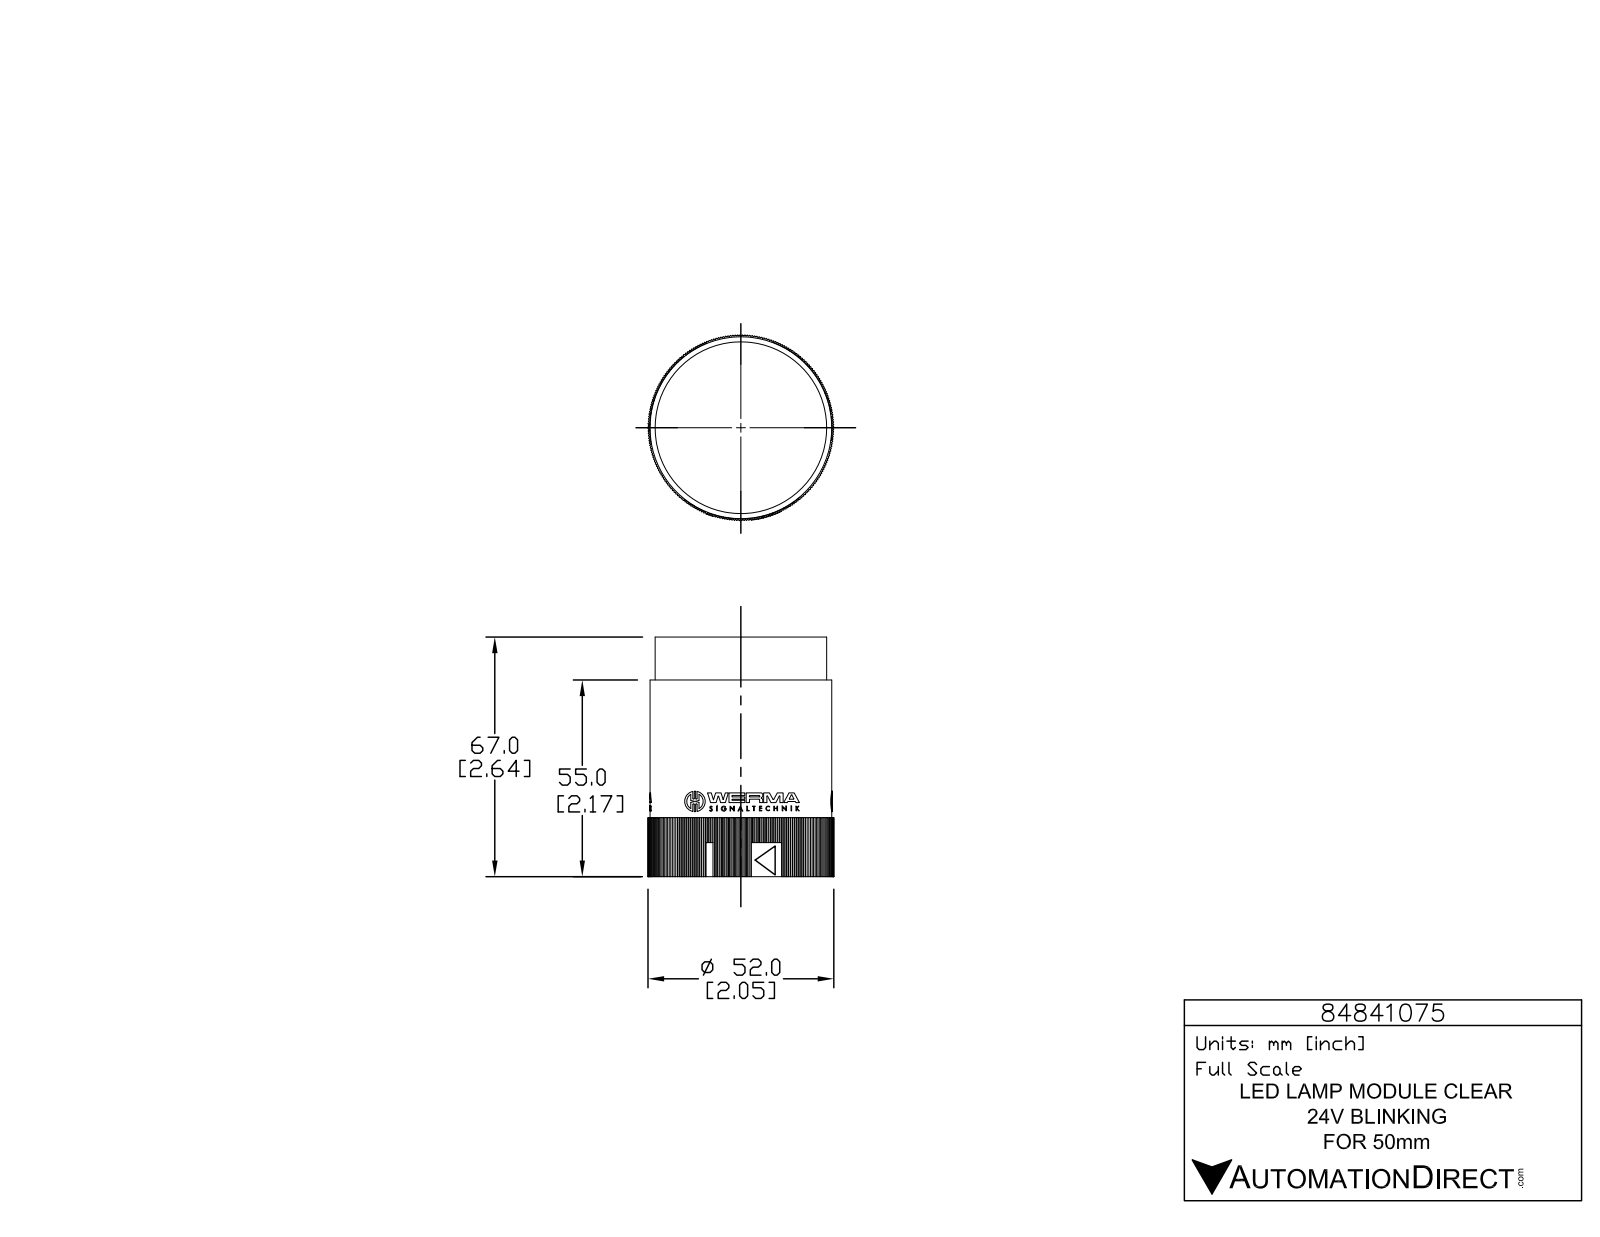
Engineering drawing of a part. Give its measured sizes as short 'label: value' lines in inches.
name: 84841075
written by: SolidWorks 2015 (AUTOMOTIVE_DESIGN)
unit: in
bodies: 1 solid, 1265 faces (1020 planar, 245 cylindrical, 0 other)
size: 2.638 × 2.047 × 2.047
volume: 6.873 in³; area: 27.62 in²
holes: 3× ⌀0.039, 1× ⌀1.898
bosses: 3× ⌀0.226, 3× ⌀0.056, 1× ⌀2.002, 1× ⌀1.89
rounds: 6× R0.008, 6× R0.008, 6× R0.008, 6× R0.131, 3× R0.004, 3× R0.005, 3× R0.008, 3× R0.008
face distances: 2.165, 1.428, 1.429, 1.429, 0.472, 2.638, 1.428, 1.428, 1.693, 1.988
